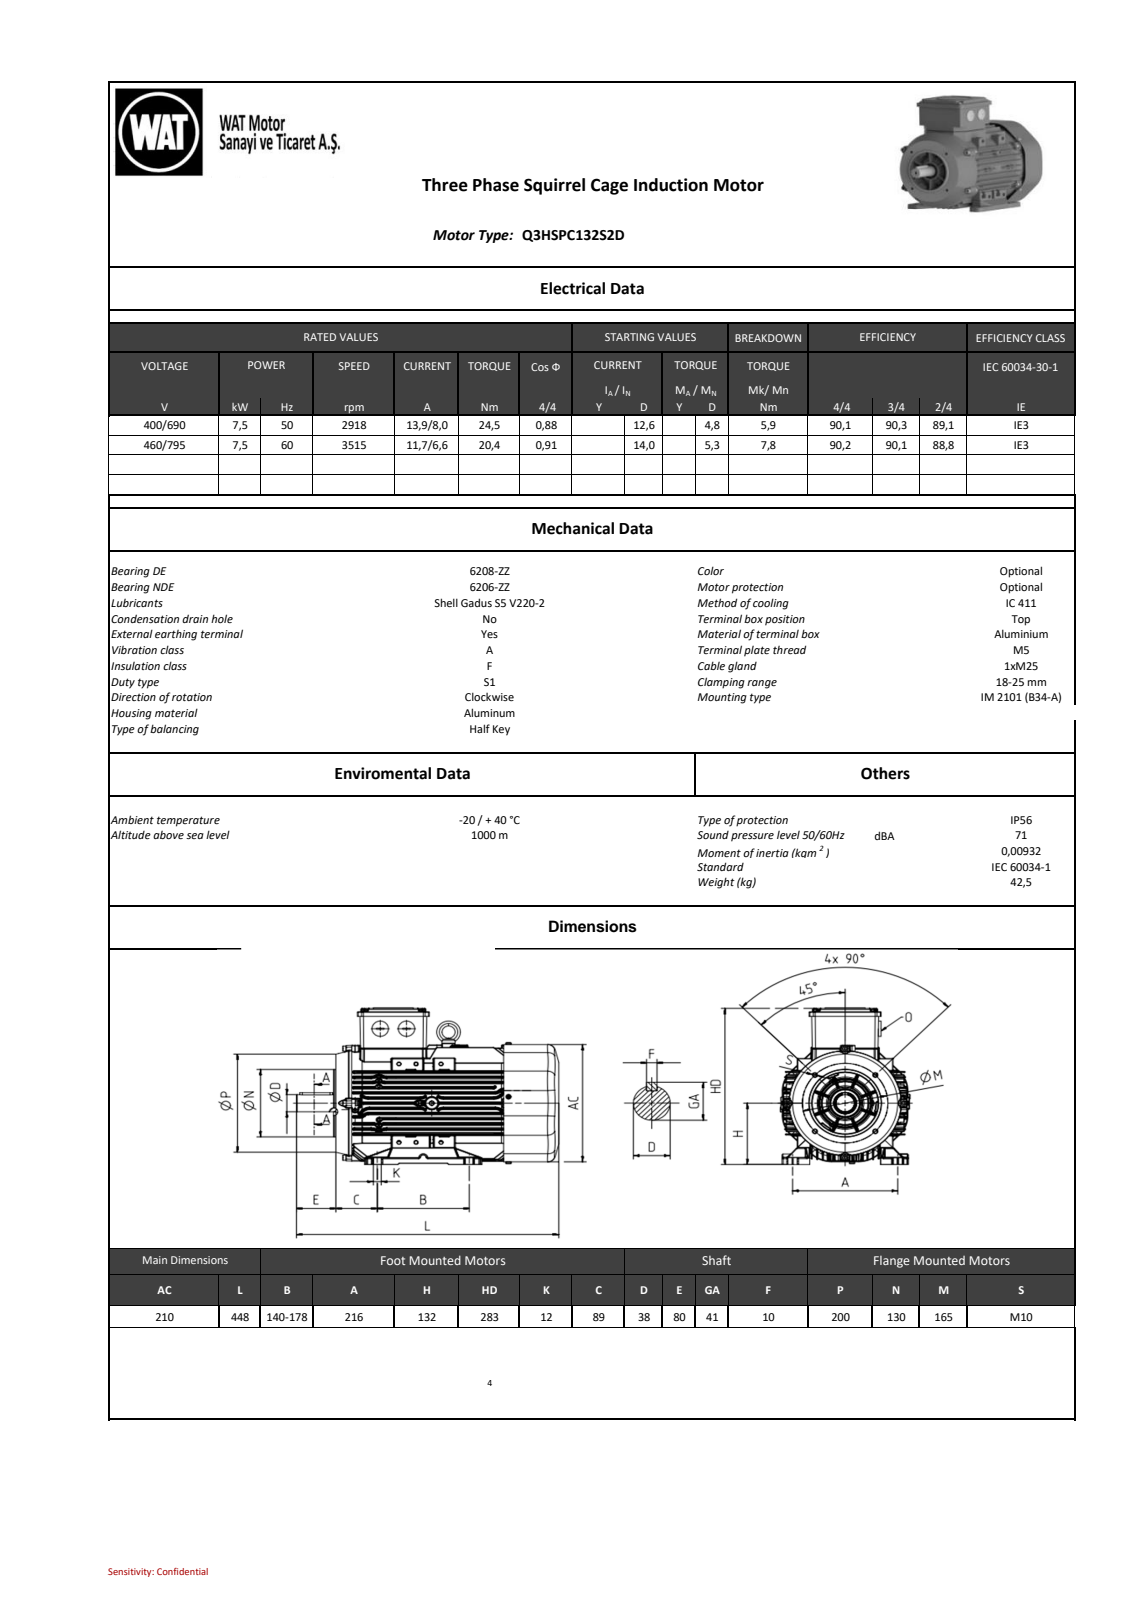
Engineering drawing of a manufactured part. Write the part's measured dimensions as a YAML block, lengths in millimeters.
part_name: "Ar311510F805552z"
step_written_by: "SIEMENS PLM Software NX 9.0 (AUTOMOTIVE_DESIGN)"
units: millimeters
bodies: {solids: 0, faces: 12019, planar: 2548, cylindrical: 3572, other: 5899}
overall_size: [447.4, 282.97, 244.67]
round_holes:
  - {diameter: 6.65, count: 4}
  - {diameter: 8.3, count: 4}
  - {diameter: 8.5, count: 4}
  - {diameter: 4.92, count: 3}
  - {diameter: 6.5, count: 2}
  - {diameter: 12, count: 2}
  - {diameter: 27.8, count: 2}
  - {diameter: 4, count: 1}
  - {diameter: 4.72, count: 1}
  - {diameter: 8, count: 1}
  - {diameter: 10.3, count: 1}
  - {diameter: 13, count: 1}
round_bosses_or_shafts:
  - {diameter: 8, count: 12}
  - {diameter: 14.8, count: 4}
  - {diameter: 13, count: 4}
  - {diameter: 11.8, count: 4}
  - {diameter: 10, count: 4}
  - {diameter: 6, count: 4}
  - {diameter: 188, count: 1}
  - {diameter: 130, count: 1}
partial_cylinders:
  - {radius: 0.5, count: 833}
  - {radius: 1, count: 674}
  - {radius: 0.8, count: 546}
  - {radius: 2, count: 240}
  - {radius: 3, count: 47}
  - {radius: 0.3, count: 24}
  - {radius: 0.38, count: 12}
  - {radius: 5, count: 12}
face_to_face_distances: [243, 1, 5, 21.5, 35.96, 10.99, 99.54, 24.97, 112.88, 8.16]
hole_center_spacings: [82.51, 40, 69.71, 110, 116.68, 165.47, 72.62, 96.5]
